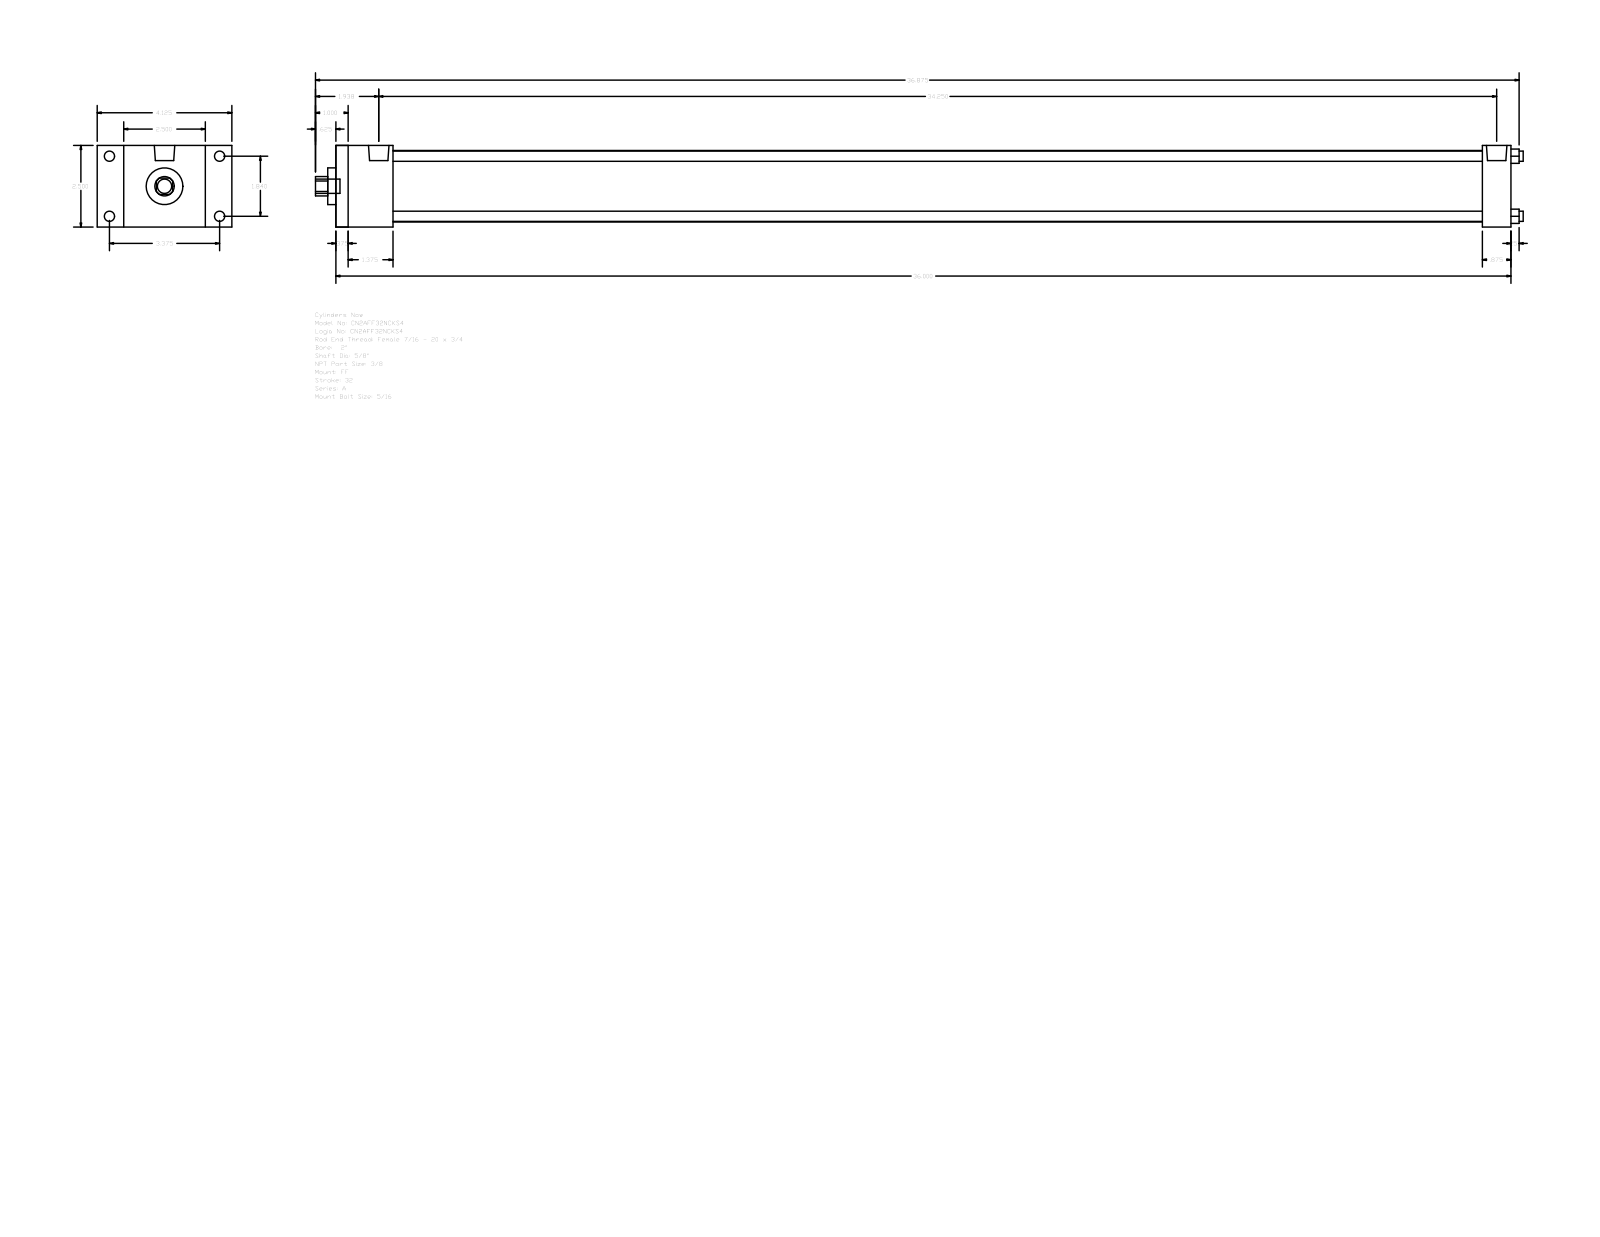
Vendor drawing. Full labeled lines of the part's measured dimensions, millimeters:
Part name (STEP PRODUCT): A_FF__0200_0.625
STEP written by: GSSL Pune (CONFIG_CONTROL_DESIGN)
Units: millimetres
Bodies: 0 solids, 92 faces (64 planar, 28 cylindrical, 0 other)
Overall size (bounding box): 939.8 × 104.78 × 63.5
Round holes (diameter × count): ⌀7.94 ×4, ⌀15.88 ×1, ⌀28.57 ×1, ⌀55.63 ×1
Round bosses / shafts (diameter × count): ⌀7.94 ×4, ⌀5.56 ×4, ⌀15.93 ×2, ⌀11.11 ×1
Partial cylindrical surfaces — rounded edges, fillets, slot ends (radius × count): R7.54 ×1
Main face-to-face distances: 63.5, 914.39, 9.52, 904.87, 44.45, 892.17, 34.93, 882.65, 847.72, 869.94
Hole centre spacings: 33.05, 46.74, 66.1
